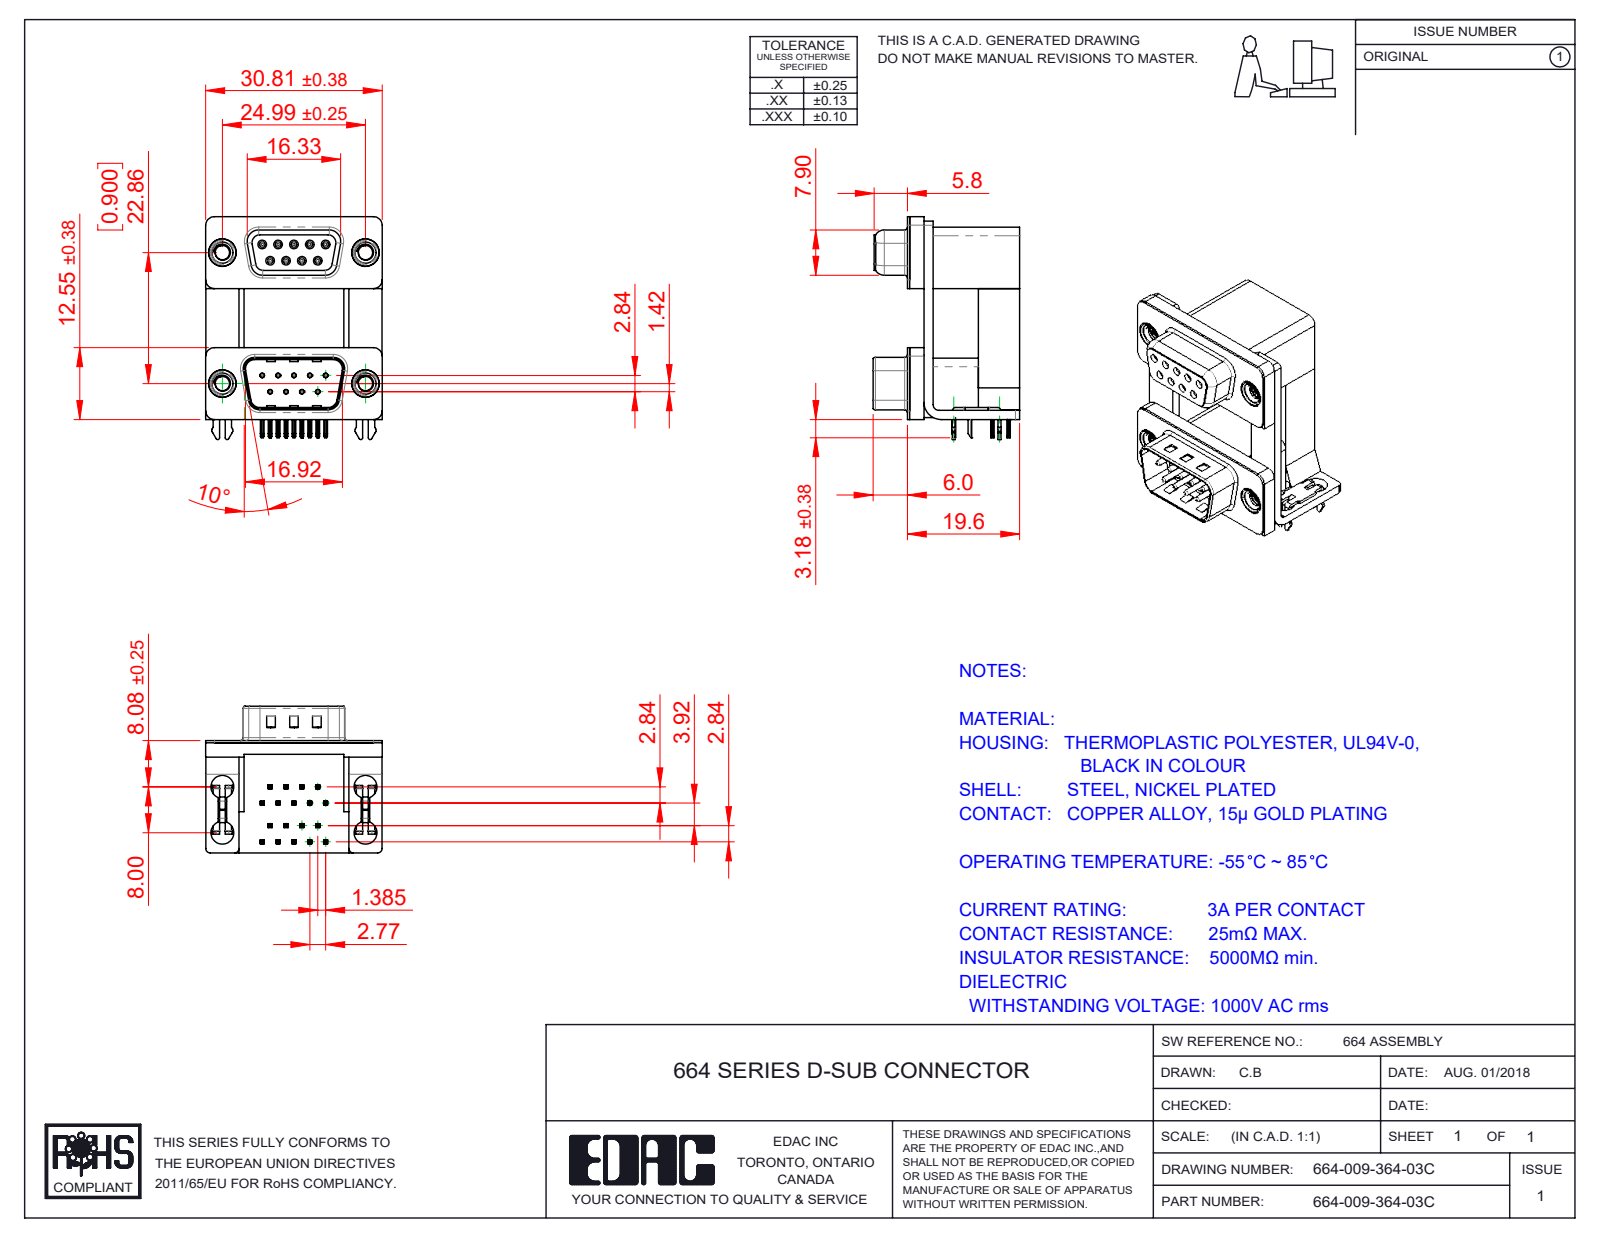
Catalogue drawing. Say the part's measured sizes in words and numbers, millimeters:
The part is named "664 Contact Top Lower; 664 Housing Upper_09 Contacts H; 664 Shell Plug_09 Contacts; 664 Contact Top Upper_H (+8 more)". Its 3-D file was written by "SolidWorks 2020 (CONFIG_CONTROL_DESIGN)". It is 31 solids with 2685 faces: 1365 planar, 753 cylindrical and 567 other. Overall it measures 38.91 by 30.81 by 25.6 millimeters. Its volume is 11 310 cubic millimeters and its surface area 13 310 square millimeters. Round holes: 18 of diameter 0.8, 9 of diameter 0.35, 9 of diameter 0.9, 8 of diameter 4, 4 of diameter 2.5, 4 of diameter 3.5, 4 of diameter 4.8, 4 of diameter 5. Round bosses or shafts: 9 of diameter 1.2, 9 of diameter 0.75, 4 of diameter 4.9, 4 of diameter 4.75, 4 of diameter 3.9. Partial cylindrical surfaces (rounded edges, fillets, slot ends): 74 of radius 0.1, 46 of radius 0.25, 36 of radius 0.15, 18 of radius 0.12, 18 of radius 0.35, 16 of radius 0.5, 13 of radius 1.5, 10 of radius 0.75. The main face-to-face distances are 0.4, 2.5, 16.7, 19.2, 12, 9.5, 7.2, 12.4, 1.6, 22.86. The hole center spacings are 3.16, 23.03, 2.77, 22.86, 23.52, 25.74, 5.54, 26.03.
